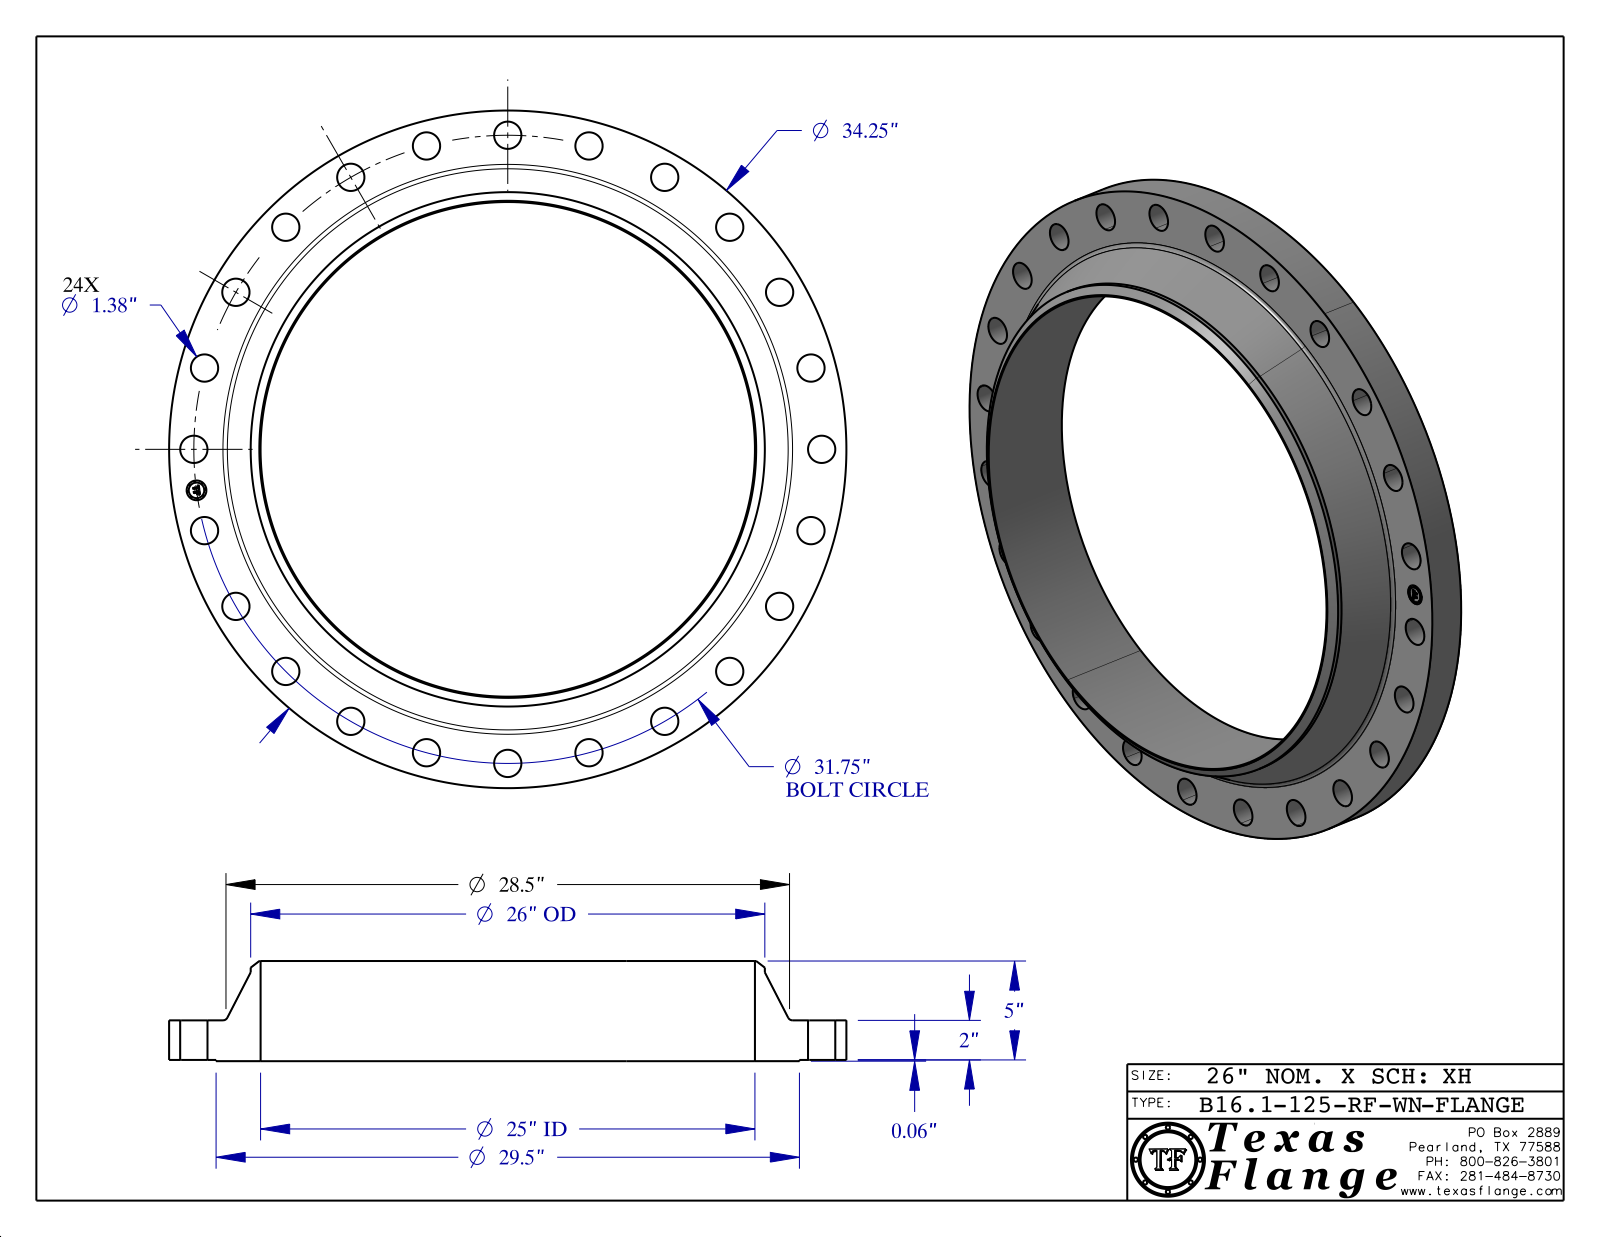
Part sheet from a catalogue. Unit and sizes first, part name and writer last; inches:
Units: inches
Overall size (bounding box): 34.25 × 34.25 × 5.063
Round holes (diameter × count): ⌀1.38 ×24, ⌀1 ×1, ⌀25 ×1
Round bosses / shafts (diameter × count): ⌀0.061 ×8, ⌀34.25 ×1, ⌀29.5 ×1, ⌀26 ×1, ⌀0.788 ×1
Main face-to-face distances: 2, 0.063, 2.063, 5.063, 5, 3, 2.048, 1.985, 0.015, 3.015
Hole centre spacings: 15.875, 15.875, 29.333, 27.496, 4.144, 8.217, 12.15, 19.328
Volume: 1 044 in³ · Surface area: 1 769 in²
Bodies: 1 solid, 451 faces (369 planar, 76 cylindrical, 6 other)
Part name (STEP PRODUCT): B16.1, Class 125-RF-WN
STEP written by: CATIA V5 STEP AP214 (AUTOMOTIVE_DESIGN)
